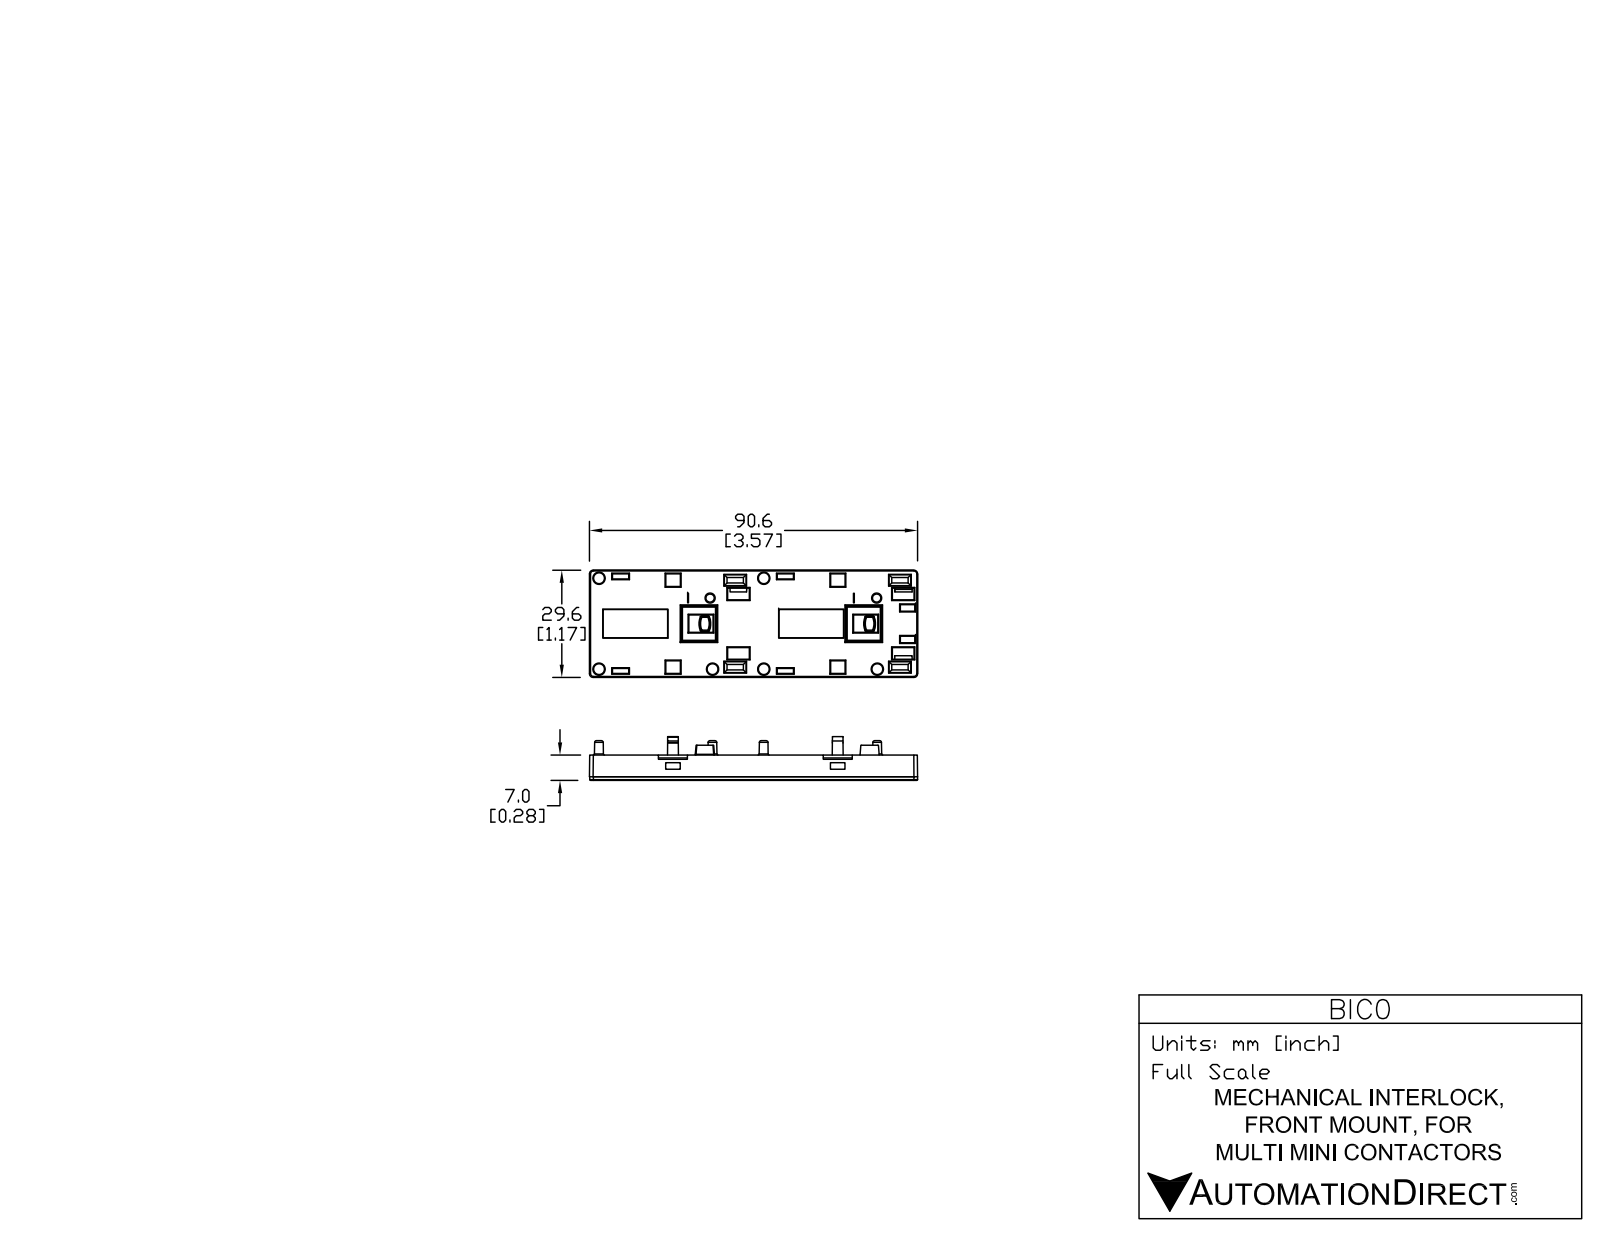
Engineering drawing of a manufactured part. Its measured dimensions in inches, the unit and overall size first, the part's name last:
Units: inches
Overall size (bounding box): 3.567 × 1.165 × 0.476
Round holes (diameter × count): ⌀0.118 ×6
Round bosses / shafts (diameter × count): ⌀0.098 ×6
Partial cylindrical surfaces — rounded edges, fillets, slot ends (radius × count): R0.007 ×4, R0.039 ×4, R0.02 ×2, R0.024 ×2
Main face-to-face distances: 0.039, 0.236, 0.276, 0.197, 1.126, 1.165, 1.087, 0.118, 0.079, 0.049
Hole centre spacings: 1.791, 0.988, 1.234, 1.581, 2.046, 0.557, 1.134, 3.026
Volume: 0.419 in³ · Surface area: 23.03 in²
Bodies: 8 solids, 381 faces (307 planar, 44 cylindrical, 30 other)
Part name (STEP PRODUCT): BIC0
STEP written by: SolidWorks 2013 (AUTOMOTIVE_DESIGN)
